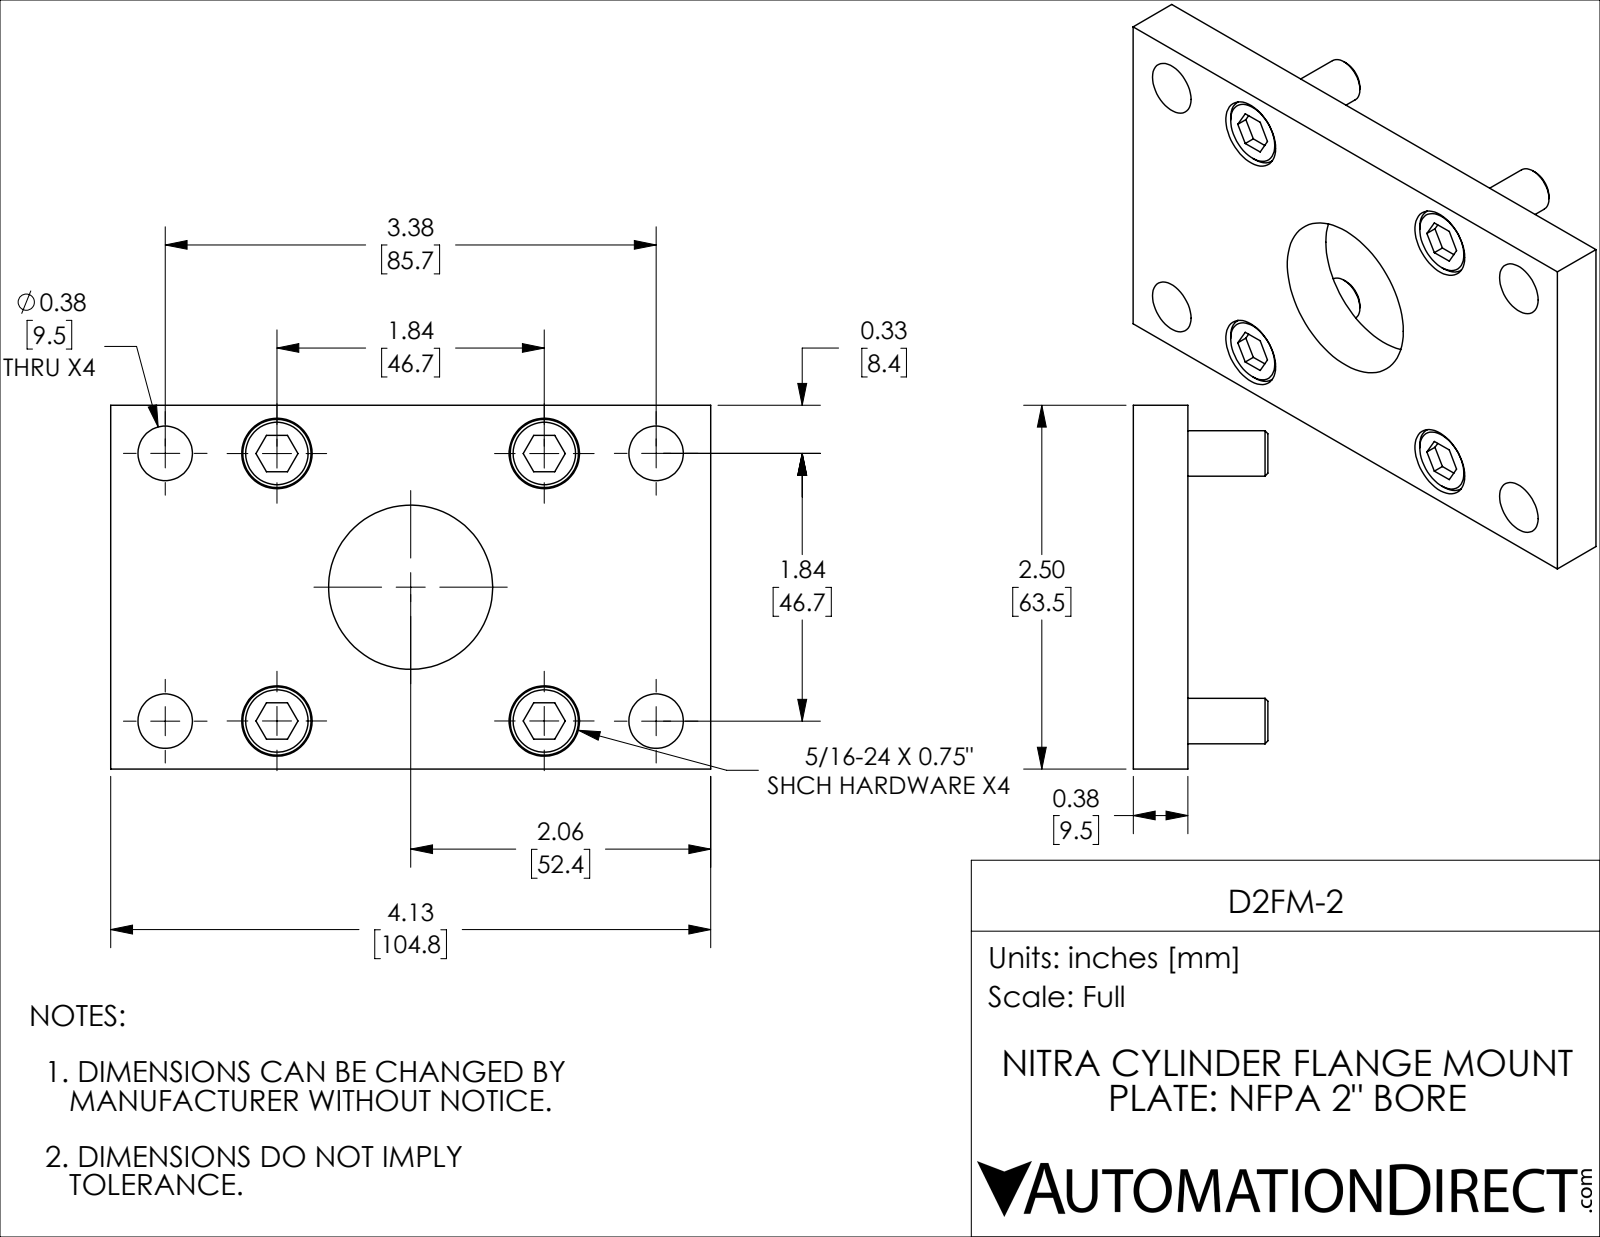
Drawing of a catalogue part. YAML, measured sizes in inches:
part_name: "D2FM-2"
step_written_by: "SolidWorks 2019 (CONFIG_CONTROL_DESIGN)"
units: inches
bodies: {solids: 5, faces: 108, planar: 50, cylindrical: 42, other: 16}
overall_size: [4.125, 2.5, 0.925]
volume: 3.442
surface_area: 32.39
round_holes:
  - {diameter: 0.343, count: 4}
  - {diameter: 0.375, count: 4}
  - {diameter: 0.484, count: 4}
  - {diameter: 1.128, count: 1}
round_bosses_or_shafts:
  - {diameter: 0.469, count: 4}
  - {diameter: 0.312, count: 4}
face_to_face_distances: [0.375, 2.5, 4.125, 0.2, 0.175, 0.078, 0.356, 0.156, 0.019, 0.55]
hole_center_spacings: [0.768, 1.3, 1.839, 1.922, 1.993, 2.607, 3.19, 1.84]
